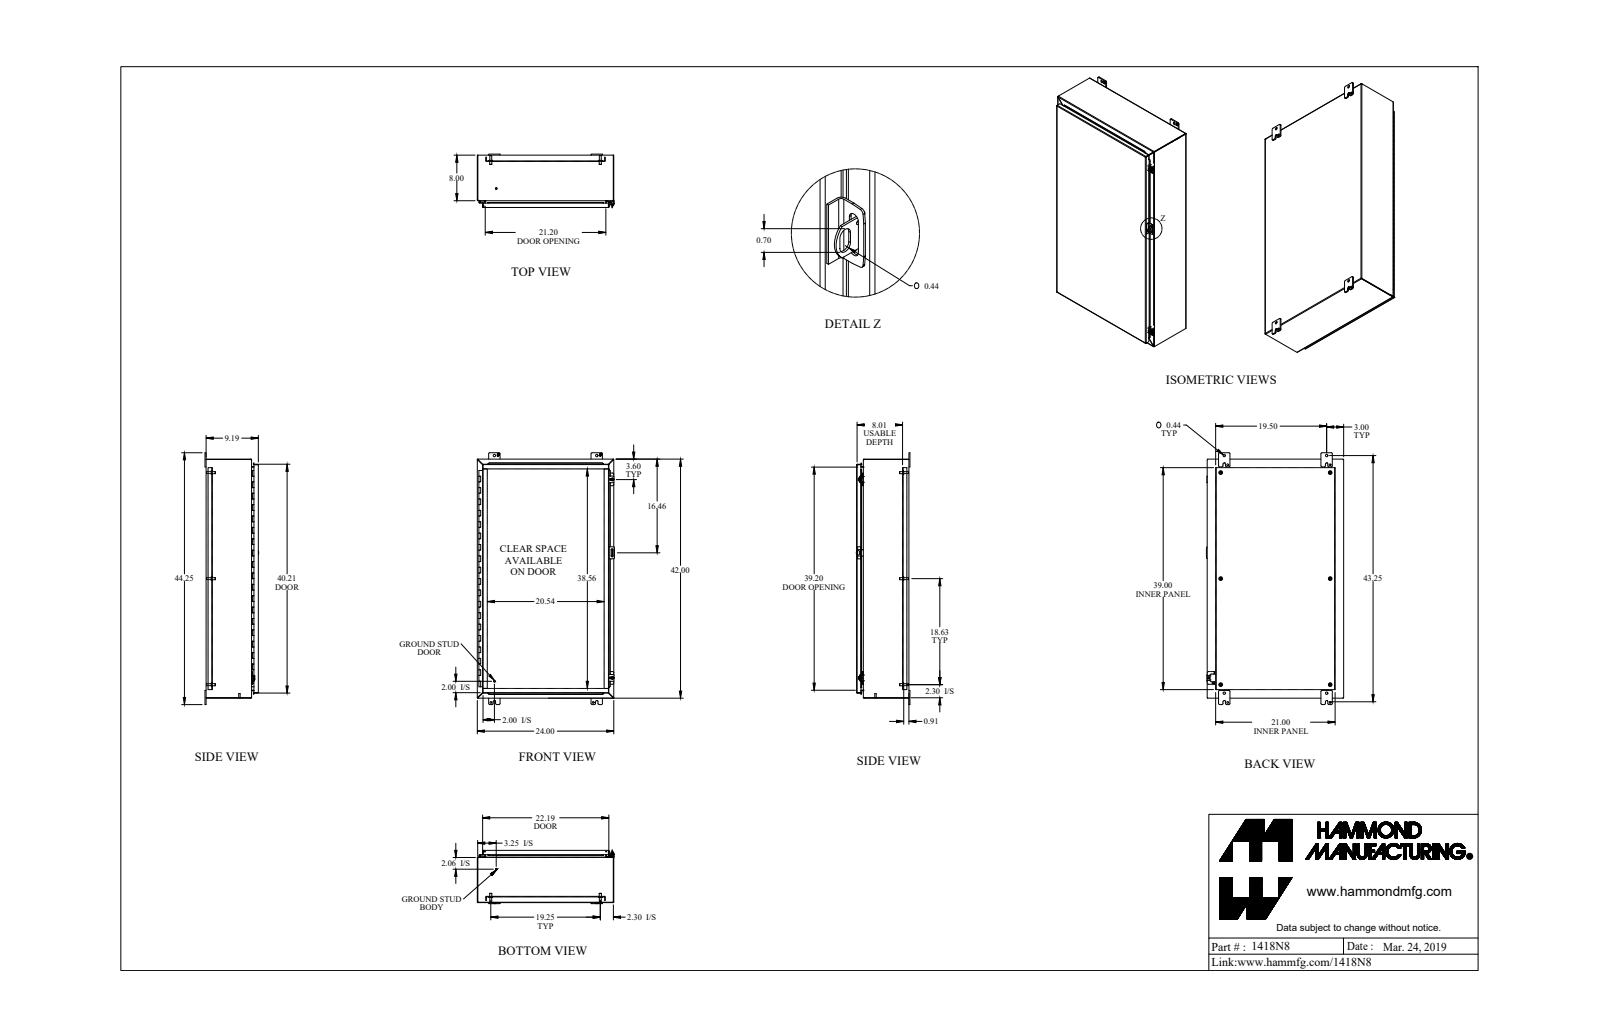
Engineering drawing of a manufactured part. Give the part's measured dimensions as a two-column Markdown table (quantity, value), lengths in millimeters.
| quantity | value |
| --- | --- |
| part name | 1418N8_Default |
| STEP written by | SolidWorks 2019 (CONFIG_CONTROL_DESIGN) |
| units | millimeters |
| bodies | 44 solids, 1399 faces (807 planar, 499 cylindrical, 93 other) |
| overall size | 1124 × 612.8 × 239.7 |
| volume | 5 806 000 mm³ |
| surface area | 5 906 000 mm² |
| round holes (diameter × count) | 12.7 × 6, 7.8 × 4, 8 × 4, 11.1 × 4, 5.4 × 2, 6.7 × 2, 9.5 × 2, 11.3 × 2, 11.3 × 2, 3.2 × 1, 4.7 × 1 |
| round bosses / shafts (diameter × count) | 16.5 × 6, 9.5 × 6, 8.4 × 6, 25.4 × 4, 12.7 × 2, 9.9 × 2, 7.1 × 2, 6.4 × 2 |
| partial cylindrical surfaces (radius × count) | 4.8 × 26, 0.9 × 24, 2.7 × 24, 1.2 × 13, 3.6 × 13, 6.4 × 12, 1 × 8, 5.5 × 8 |
| main face-to-face distances | 1.8, 231.5, 229.6, 23.8, 233.3, 2.4, 25.6, 205.3, 203.4, 26.2 |
| hole center spacings | 489, 680.3, 457.2, 473.1, 473.1, 946.2, 44.1, 61.8 |
